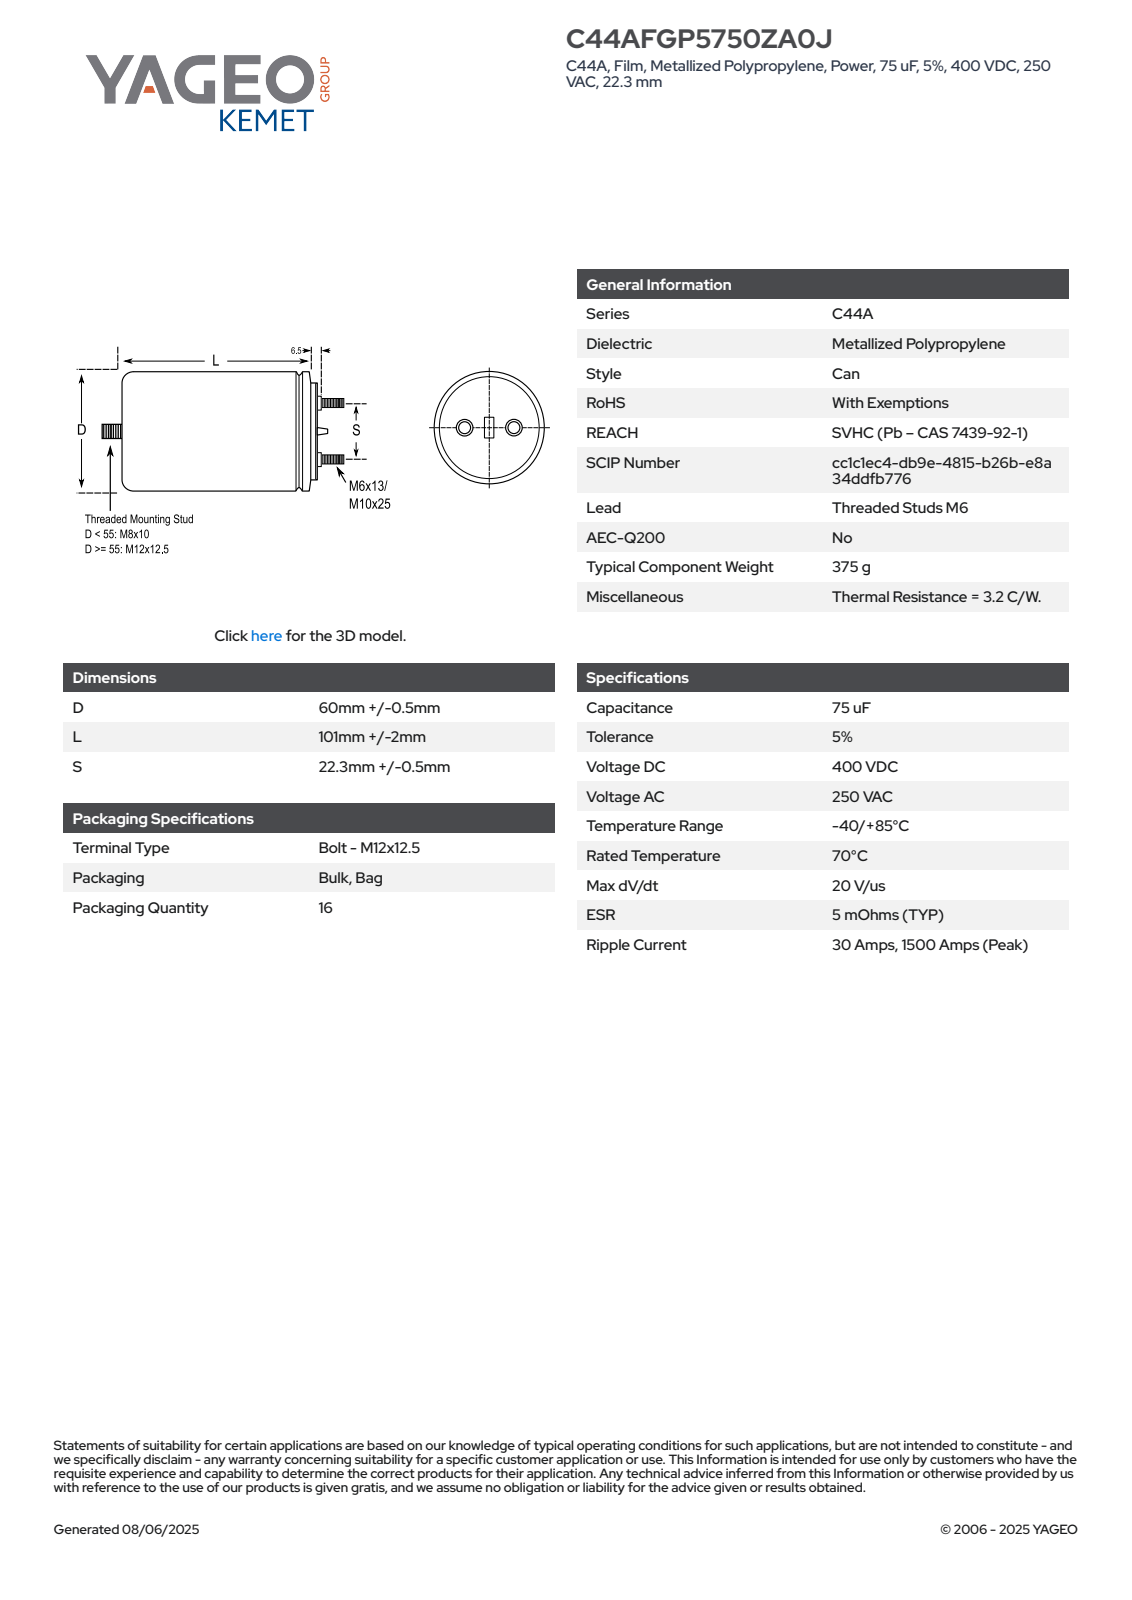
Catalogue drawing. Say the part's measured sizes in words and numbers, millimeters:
The part is named "CFP_C44A_60X101_D60.5L103S22.3". Its 3-D file was written by "SolidWorks 2014 (AUTOMOTIVE_DESIGN)". It is 1 solid with 102 faces: 29 planar, 34 cylindrical and 39 other. Overall it measures 135 by 60.5 by 60.5 millimeters. Its volume is 305 000 cubic millimeters and its surface area 26 938 square millimeters. Round bosses or shafts: 2 of diameter 9, 2 of diameter 6, 1 of diameter 60.5, 1 of diameter 47.45, 1 of diameter 12. Partial cylindrical surfaces (rounded edges, fillets, slot ends): 1 of radius 30.24. The main face-to-face distances are 108, 12.5, 120.5, 122, 109.5, 1.5, 135, 122.5, 14.5, 13.
